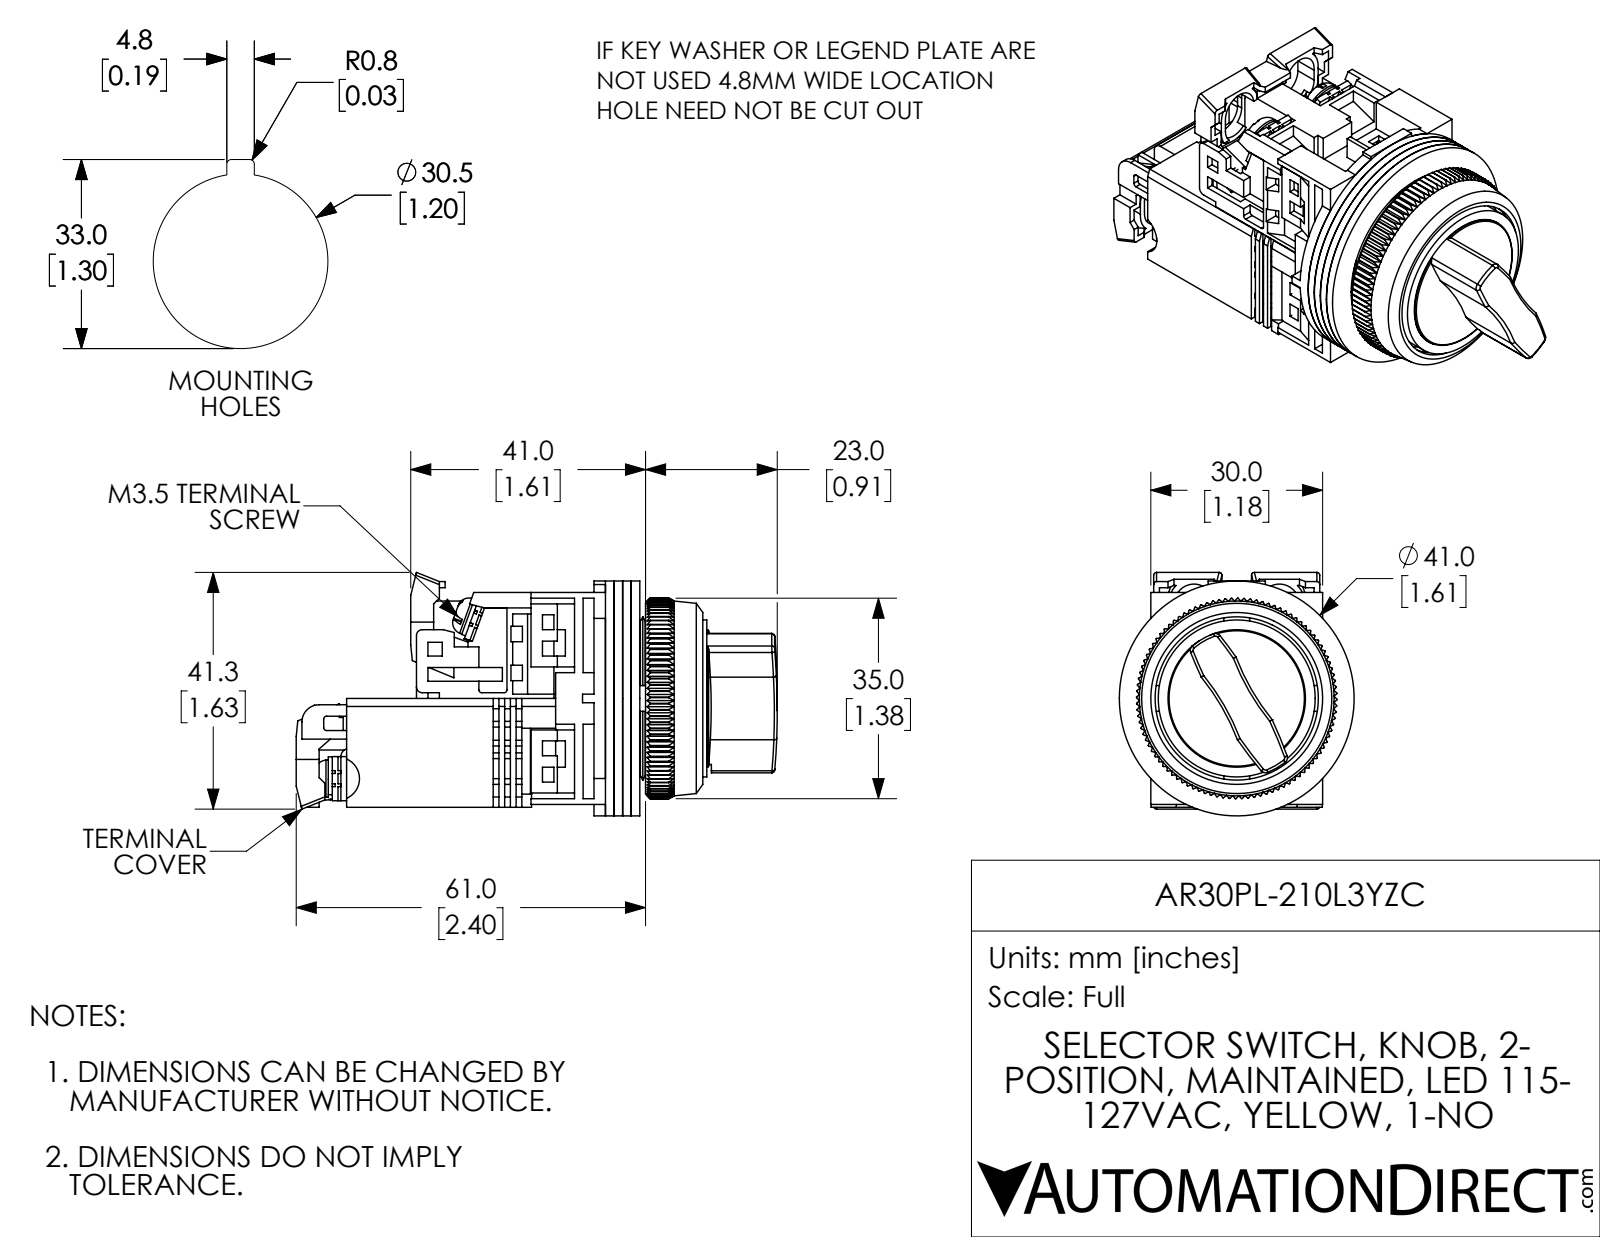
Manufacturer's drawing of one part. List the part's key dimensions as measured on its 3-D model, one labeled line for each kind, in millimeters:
Part name (STEP PRODUCT): AR30PL-210L3YZC
STEP written by: SolidWorks 2017 (AUTOMOTIVE_DESIGN)
Units: millimetres
Bodies: 27 solids, 2357 faces (1706 planar, 321 cylindrical, 330 other)
Overall size (bounding box): 84 × 42.5 × 41
Volume: 49 180 mm³ · Surface area: 40 890 mm²
Round holes (diameter × count): ⌀3.5 ×6, ⌀3.6 ×4, ⌀3 ×3, ⌀12 ×1, ⌀18 ×1, ⌀19.5 ×1, ⌀21 ×1, ⌀28.5 ×1, ⌀30 ×1, ⌀31.8 ×1
Round bosses / shafts (diameter × count): ⌀6.6 ×4, ⌀3.5 ×2, ⌀1.6 ×2, ⌀41 ×1, ⌀29.2 ×1, ⌀27.4 ×1, ⌀24 ×1, ⌀22.5 ×1
Partial cylindrical surfaces — rounded edges, fillets, slot ends (radius × count): R1.5 ×17, R0.5 ×13, R1 ×6, R3.5 ×4, R4.5 ×4, R3 ×2, R40 ×2, R75 ×2
Main face-to-face distances: 1.5, 3, 4.5, 2, 1, 19, 20, 5, 6.5, 36
Hole centre spacings: 14.7, 7.5, 15.8, 0.5, 7.7, 14.8, 14.8, 15.4
